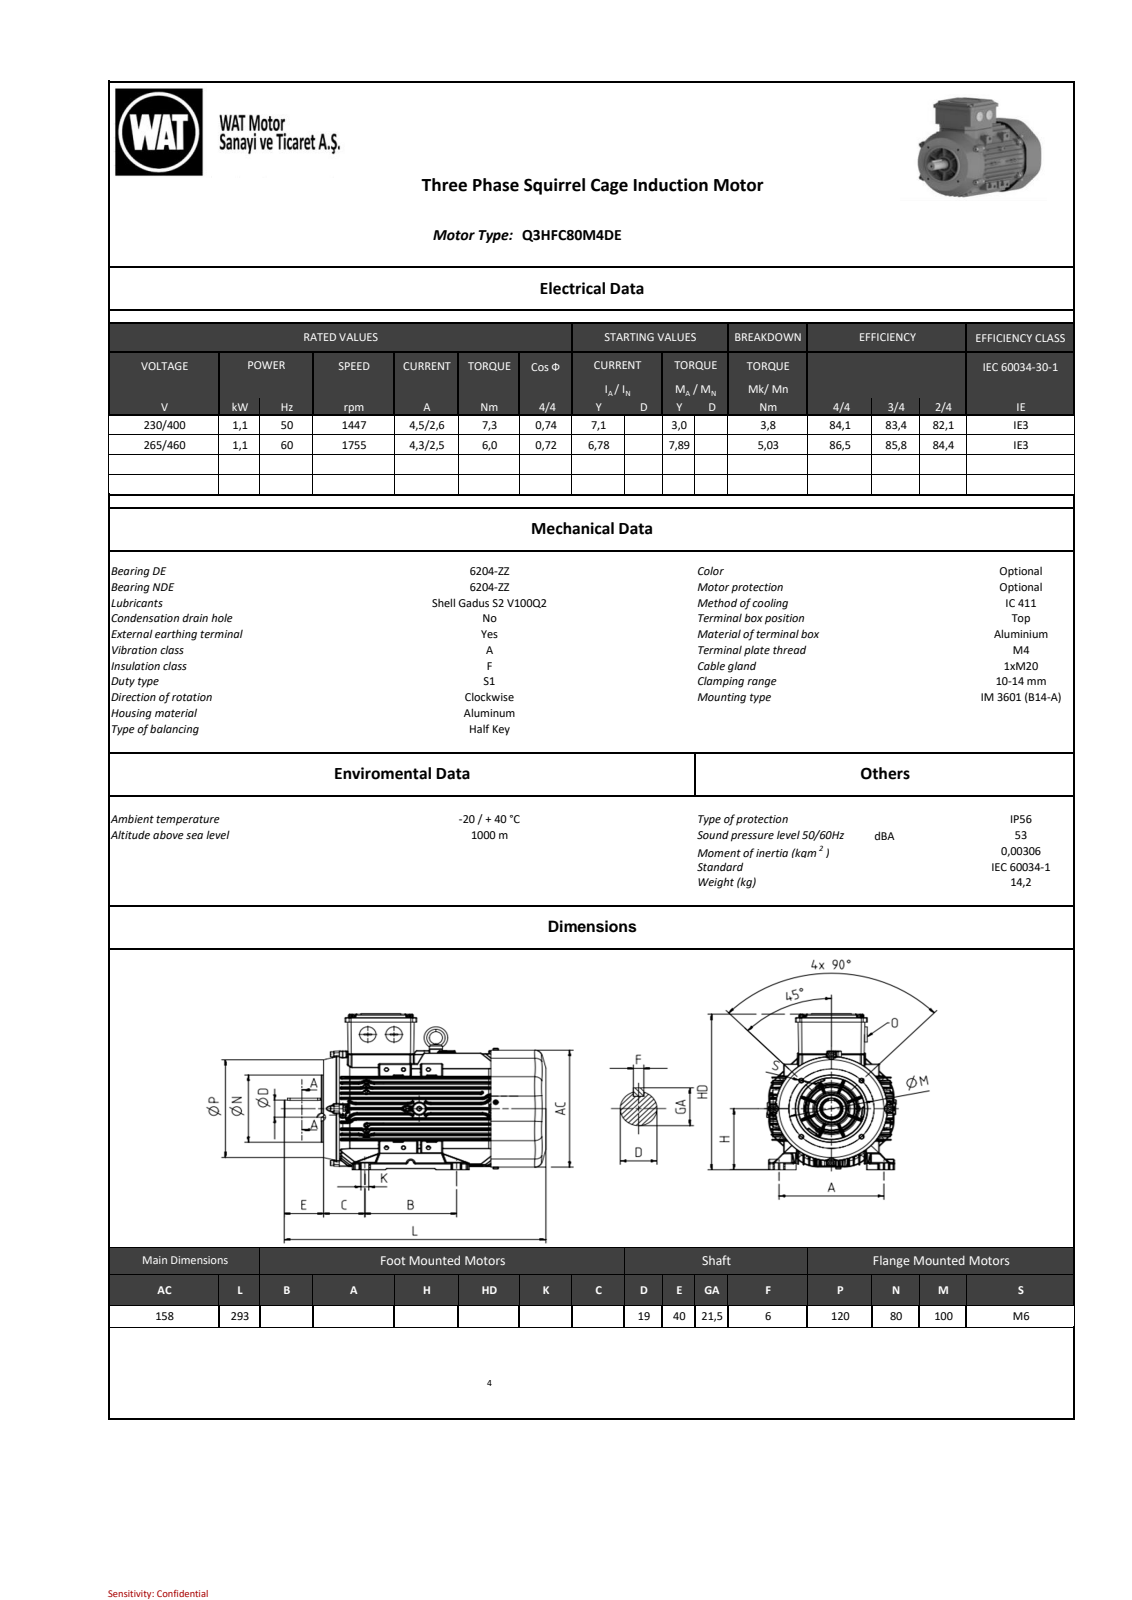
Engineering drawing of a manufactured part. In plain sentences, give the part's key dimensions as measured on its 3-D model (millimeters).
The part is named "model1". Its 3-D file was written by "SIEMENS PLM Software NX2206.8101 (AUTOMOTIVE_DESIGN)". It is 0 solids with 5291 faces: 1085 planar, 1548 cylindrical and 2658 other. Overall it measures 293 by 214.5 by 158 millimeters. Round holes: 3 of diameter 3, 2 of diameter 3.5, 2 of diameter 4.6, 2 of diameter 5, 1 of diameter 3.3, 1 of diameter 8, 1 of diameter 51, 1 of diameter 57. Round bosses or shafts: 5 of diameter 6, 3 of diameter 8.33, 2 of diameter 21.38, 1 of diameter 146.5, 1 of diameter 80, 1 of diameter 61, 1 of diameter 30, 1 of diameter 24.07. Partial cylindrical surfaces (rounded edges, fillets, slot ends): 555 of radius 0.5, 281 of radius 0.8, 170 of radius 1, 21 of radius 2, 12 of radius 5, 8 of radius 75.75, 4 of radius 2.25, 4 of radius 3.5. The main face-to-face distances are 1, 41.96, 157, 156.98, 10.36, 86, 10.49, 52.32, 18, 221. The hole center spacings are 25.5, 44.17, 44.16, 50.3, 54.45, 70.94.
